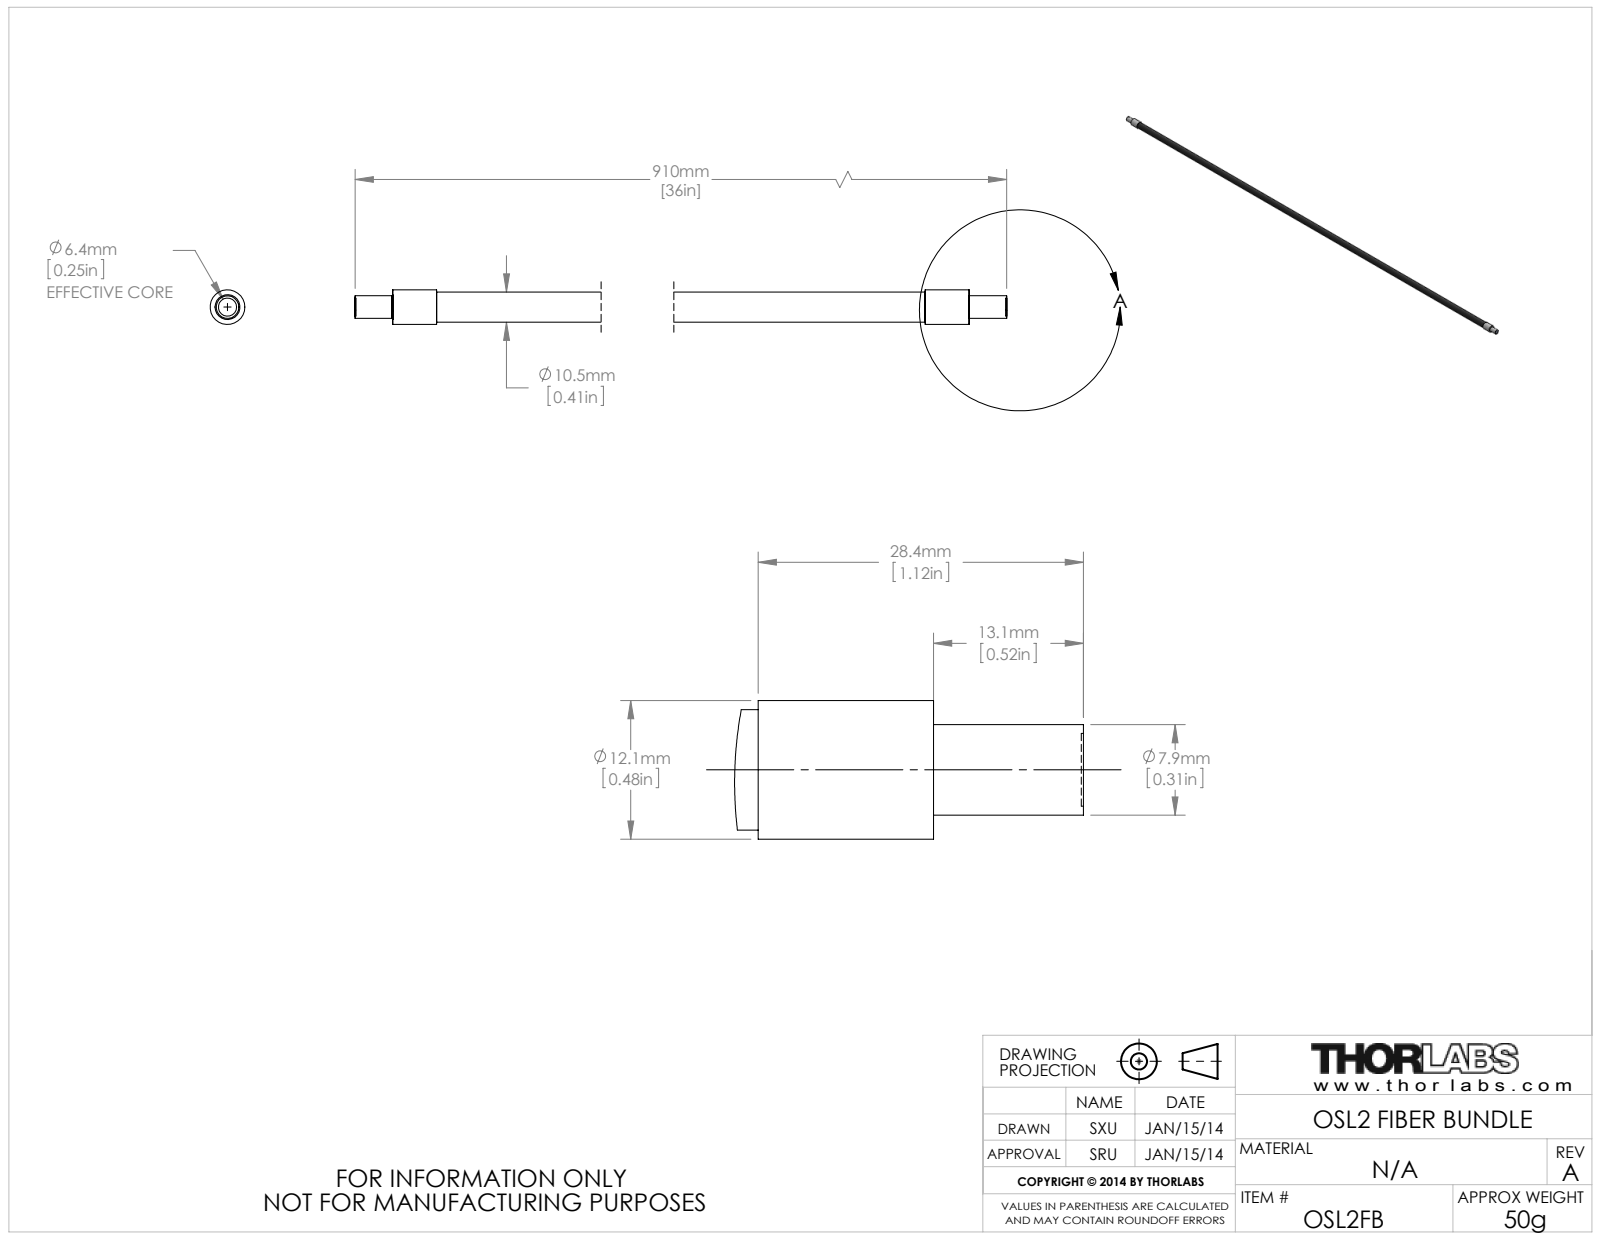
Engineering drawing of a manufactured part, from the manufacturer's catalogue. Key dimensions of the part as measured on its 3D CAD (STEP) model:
Part name (STEP PRODUCT): CTN002086-E0W
STEP written by: SolidWorks 2014 (CONFIG_CONTROL_DESIGN)
Units: millimetres
Bodies: 1 solid, 24 faces (8 planar, 14 cylindrical, 2 other)
Overall size (bounding box): 910 × 12.1 × 12.1
Volume: 78 670 mm³ · Surface area: 30 248 mm²
Round holes (diameter × count): ⌀6.35 ×1
Round bosses / shafts (diameter × count): ⌀12.1 ×1, ⌀10.5 ×1, ⌀7.9 ×1
Main face-to-face distances: 12.9, 896.7, 28.2, 881.4, 15.3, 868.5, 883.8, 13.1, 28.4, 881.6
